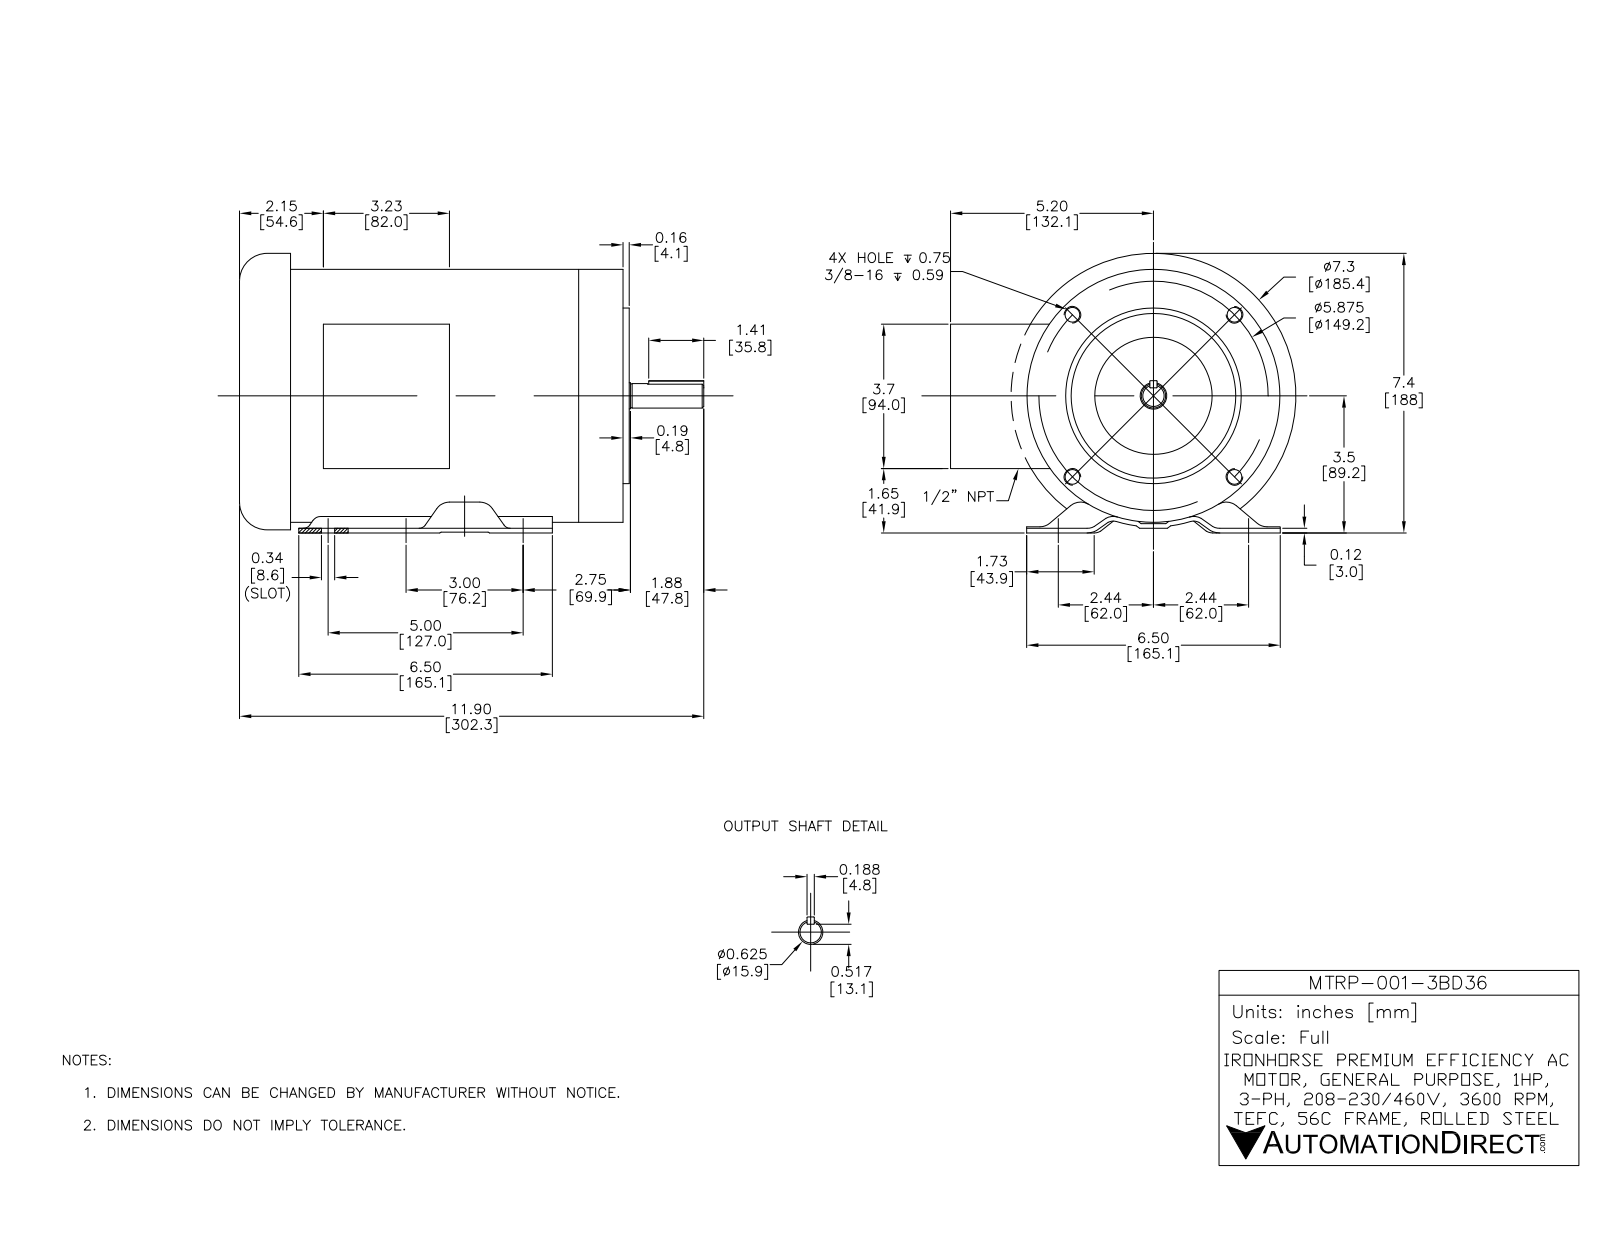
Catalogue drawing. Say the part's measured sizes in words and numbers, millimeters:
The part is named "MTRP-001-BD36". Its 3-D file was written by "SolidWorks 2016 (AUTOMOTIVE_DESIGN)". It is 40 solids with 3663 faces: 821 planar, 1174 cylindrical and 1668 other. Overall it measures 299.1 by 227.03 by 183.73 millimeters. Its volume is 728 366 cubic millimeters and its surface area 624 276 square millimeters. Round holes: 12 of diameter 5, 9 of diameter 5.56, 9 of diameter 7, 6 of diameter 5.5, 6 of diameter 6.93, 6 of diameter 8.73, 5 of diameter 3.45, 4 of diameter 3.8, 4 of diameter 4.5, 4 of diameter 7.94, 2 of diameter 1.7, 2 of diameter 3.4. Round bosses or shafts: 9 of diameter 8.84, 9 of diameter 4.17, 6 of diameter 10.52, 6 of diameter 6.35, 6 of diameter 4.83, 1 of diameter 182.5, 1 of diameter 164, 1 of diameter 114.3. Partial cylindrical surfaces (rounded edges, fillets, slot ends): 204 of radius 0.5, 123 of radius 3, 43 of radius 2, 38 of radius 1, 32 of radius 4, 26 of radius 3.5, 19 of radius 7, 12 of radius 4.37. The main face-to-face distances are 3, 1, 1.6, 245, 244, 2, 90.4, 78.4, 1.2, 2.5. The hole center spacings are 107.22, 77, 2.39, 58.93, 61.2, 74.61, 75.67, 95.21.
